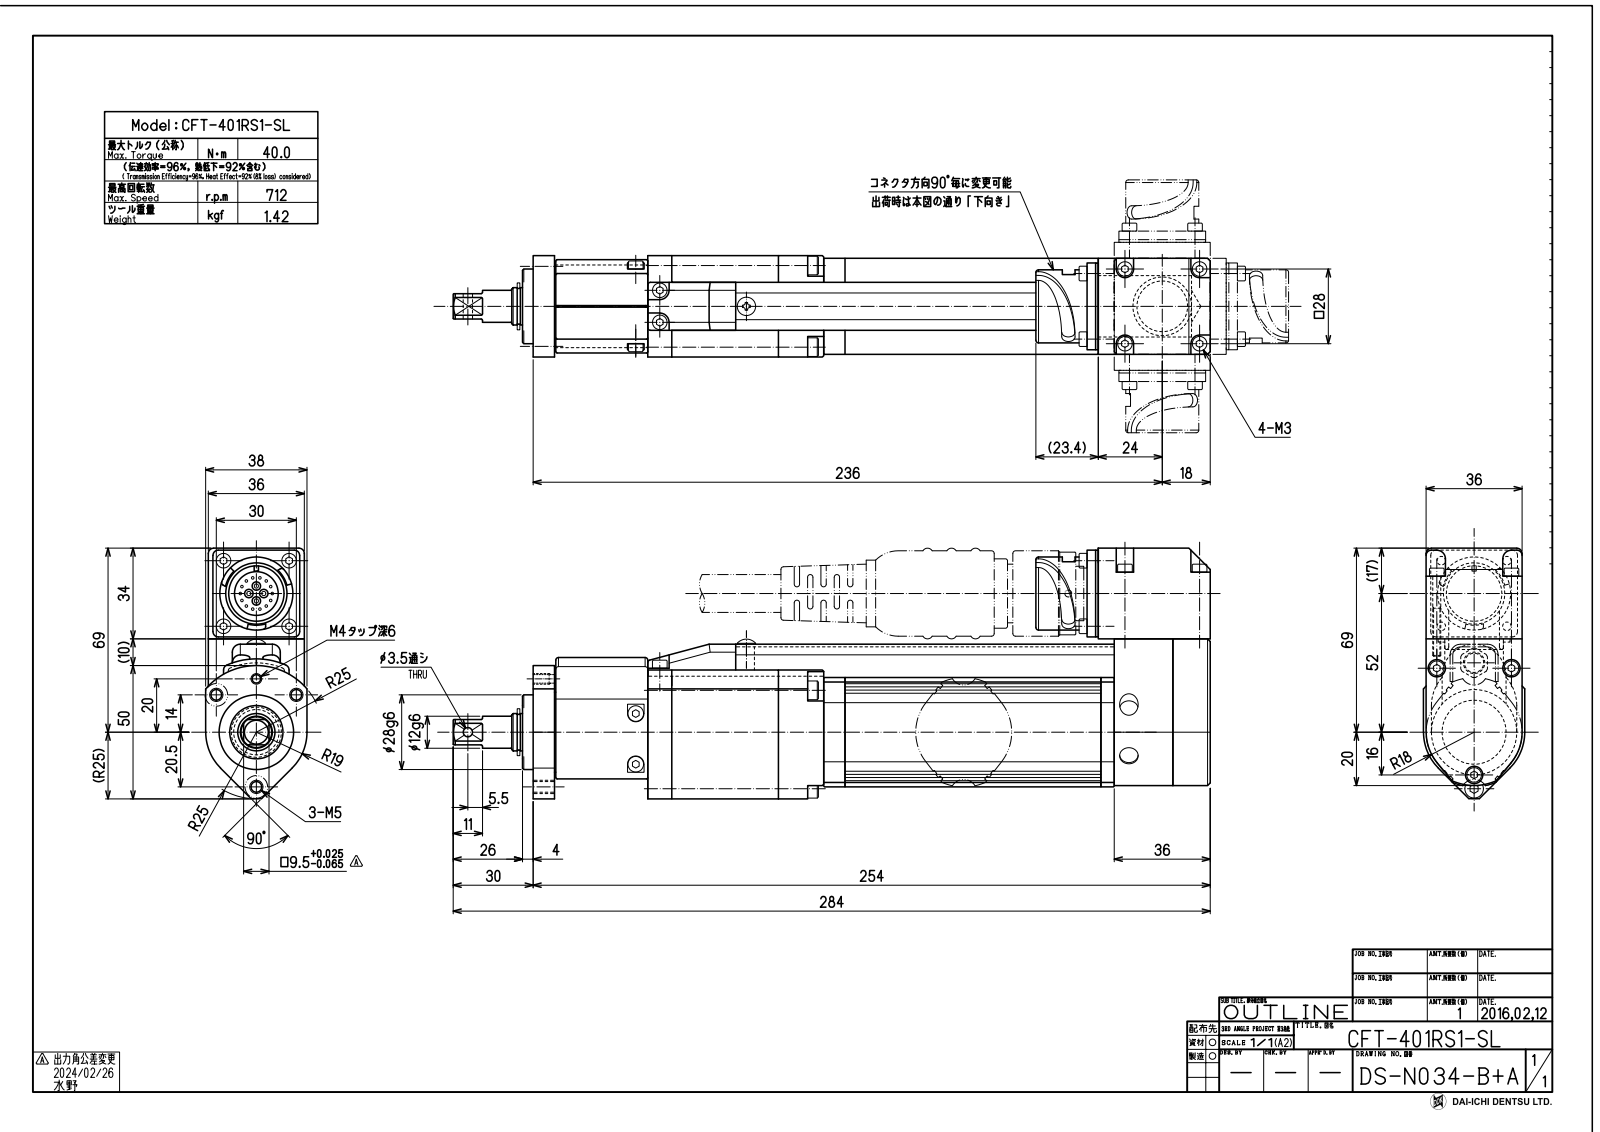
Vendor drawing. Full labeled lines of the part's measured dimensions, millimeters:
Part name (STEP PRODUCT): CFT-401RS1-SL
STEP written by: SolidWorks 2015 (CONFIG_CONTROL_DESIGN)
Units: millimetres
Bodies: 34 solids, 438 faces (215 planar, 150 cylindrical, 73 other)
Overall size (bounding box): 284 × 94 × 38
Volume: 428 331 mm³ · Surface area: 96 450 mm²
Round holes (diameter × count): ⌀4.2 ×3, ⌀3.3 ×1, ⌀3.5 ×1, ⌀20.4 ×1
Round bosses / shafts (diameter × count): ⌀5.5 ×10, ⌀6 ×3, ⌀28 ×1, ⌀27.4 ×1, ⌀17.6 ×1, ⌀14 ×1, ⌀13.4 ×1, ⌀12 ×1
Partial cylindrical surfaces — rounded edges, fillets, slot ends (radius × count): R0.5 ×8, R3 ×8, R18 ×4, R20.5 ×4, R2 ×2, R3.02 ×2, R3.25 ×2, R3.5 ×2
Main face-to-face distances: 18, 109, 36, 9, 1, 40, 162, 8, 101, 23
Hole centre spacings: 16.16, 37.62, 40.85, 30, 32, 40.5, 72.5
